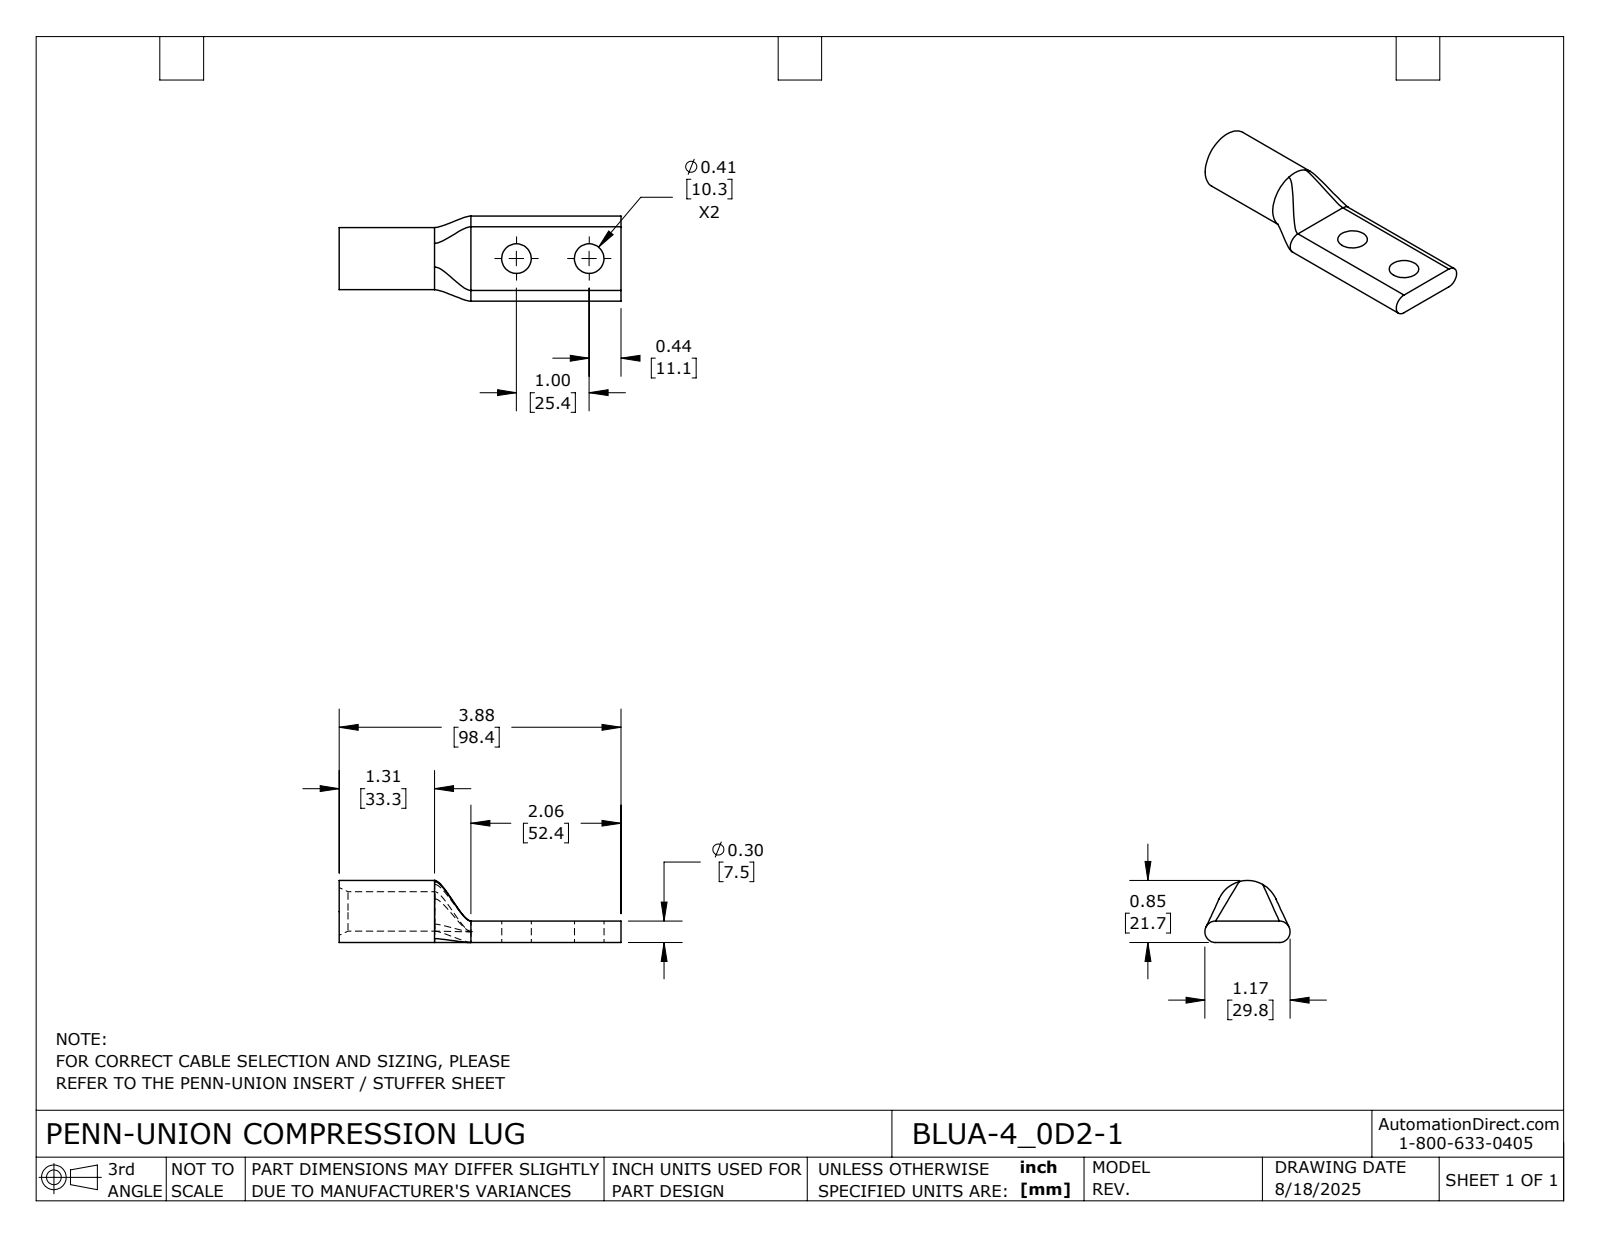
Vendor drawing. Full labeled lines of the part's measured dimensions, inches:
Part name (STEP PRODUCT): BLUA-4_0D2-1
STEP written by: SolidWorks 2024 (CONFIG_CONTROL_DESIGN)
Units: inches
Bodies: 1 solid, 26 faces (5 planar, 11 cylindrical, 10 other)
Overall size (bounding box): 3.875 × 1.172 × 0.854
Volume: 1.211 in³ · Surface area: 14.7 in²
Round holes (diameter × count): ⌀0.406 ×2, ⌀0.542 ×1
Round bosses / shafts (diameter × count): ⌀0.854 ×1
Partial cylindrical surfaces — rounded edges, fillets, slot ends (radius × count): R0.148 ×2
Main face-to-face distances: 0.297, 3.875, 1.813, 2.062
Hole centre spacings: 1
